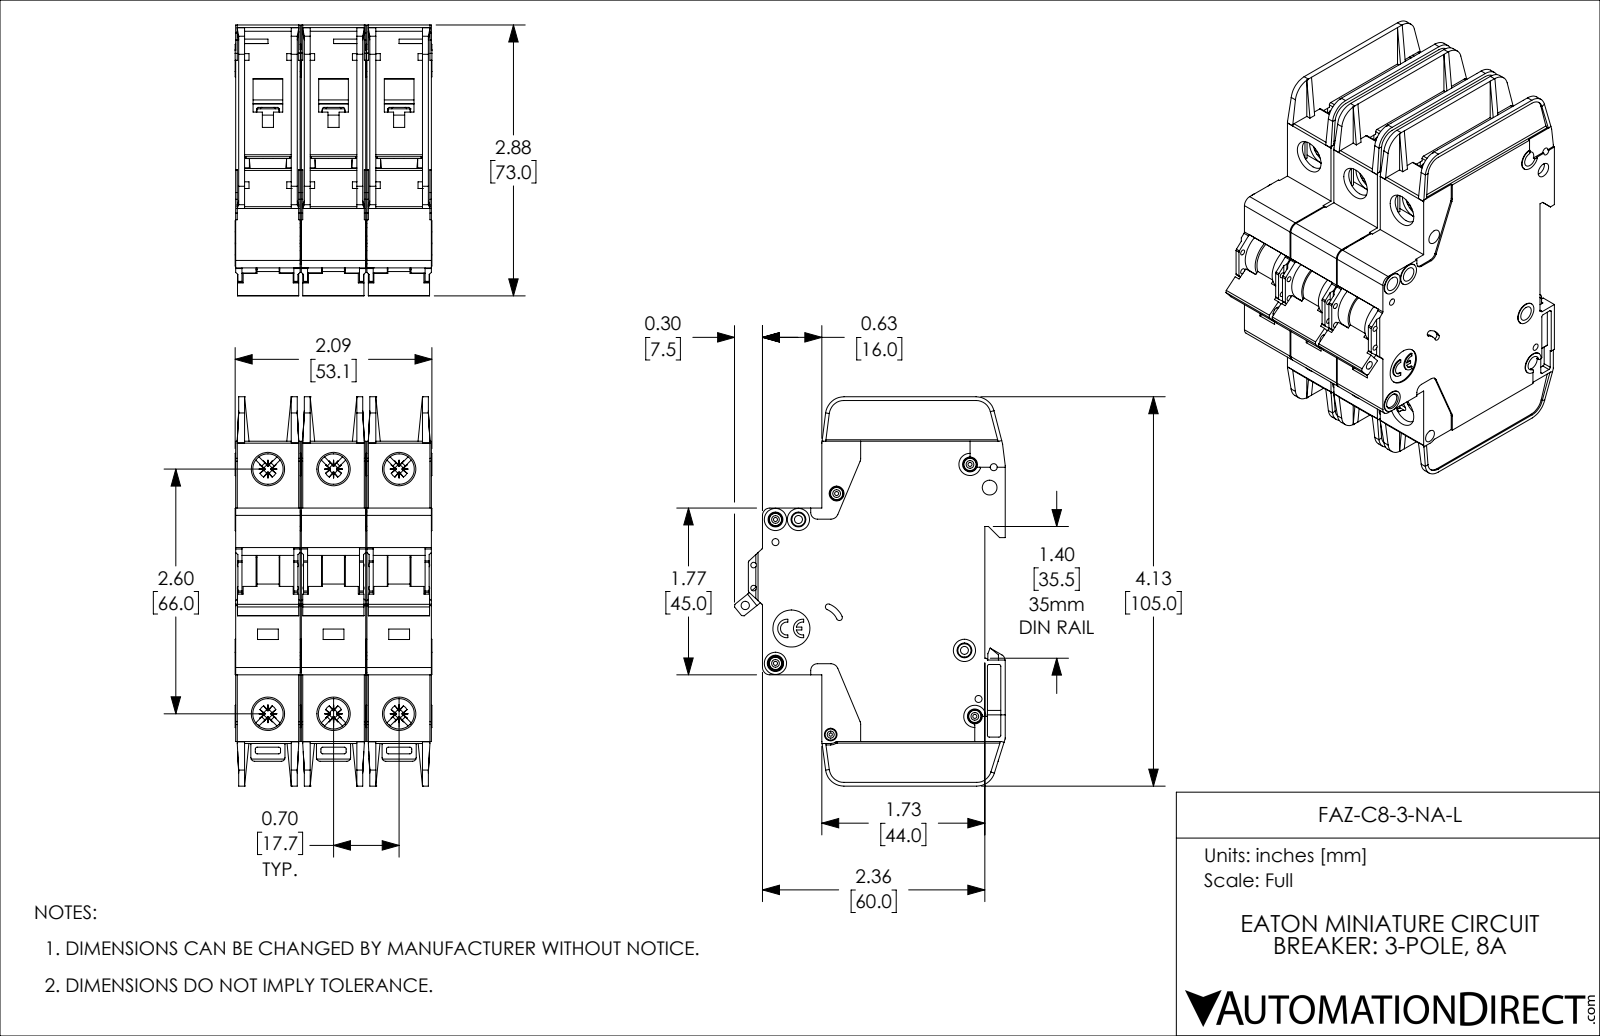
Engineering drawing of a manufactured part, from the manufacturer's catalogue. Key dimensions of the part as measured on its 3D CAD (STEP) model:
Part name (STEP PRODUCT): FAZ-C8-3-NA-L
STEP written by: SolidWorks 2019 (AUTOMOTIVE_DESIGN)
Units: inches
Bodies: 3 solids, 3381 faces (2013 planar, 1071 cylindrical, 297 other)
Overall size (bounding box): 4.134 × 2.876 × 2.091
Volume: 14.05 in³ · Surface area: 123 in²
Round holes (diameter × count): ⌀0.157 ×8, ⌀0.323 ×6, ⌀0.043 ×5, ⌀0.075 ×4, ⌀0.059 ×2, ⌀0.085 ×2, ⌀0.035 ×1, ⌀0.089 ×1, ⌀0.098 ×1, ⌀0.134 ×1, ⌀0.394 ×1
Round bosses / shafts (diameter × count): ⌀0.13 ×5, ⌀0.236 ×4, ⌀0.118 ×4, ⌀0.098 ×3
Partial cylindrical surfaces — rounded edges, fillets, slot ends (radius × count): R0.02 ×72, R0.016 ×30, R0.039 ×18, R0.043 ×12, R0.079 ×12, R0.008 ×6, R0.01 ×6, R0.028 ×6
Main face-to-face distances: 0.697, 0.047, 1.394, 0.685, 0.591, 1.382, 0.744, 0.65, 0.106, 0.094
Hole centre spacings: 0.697, 2.69, 2.598, 0.244, 0.537, 0.87, 1.394, 2.948
